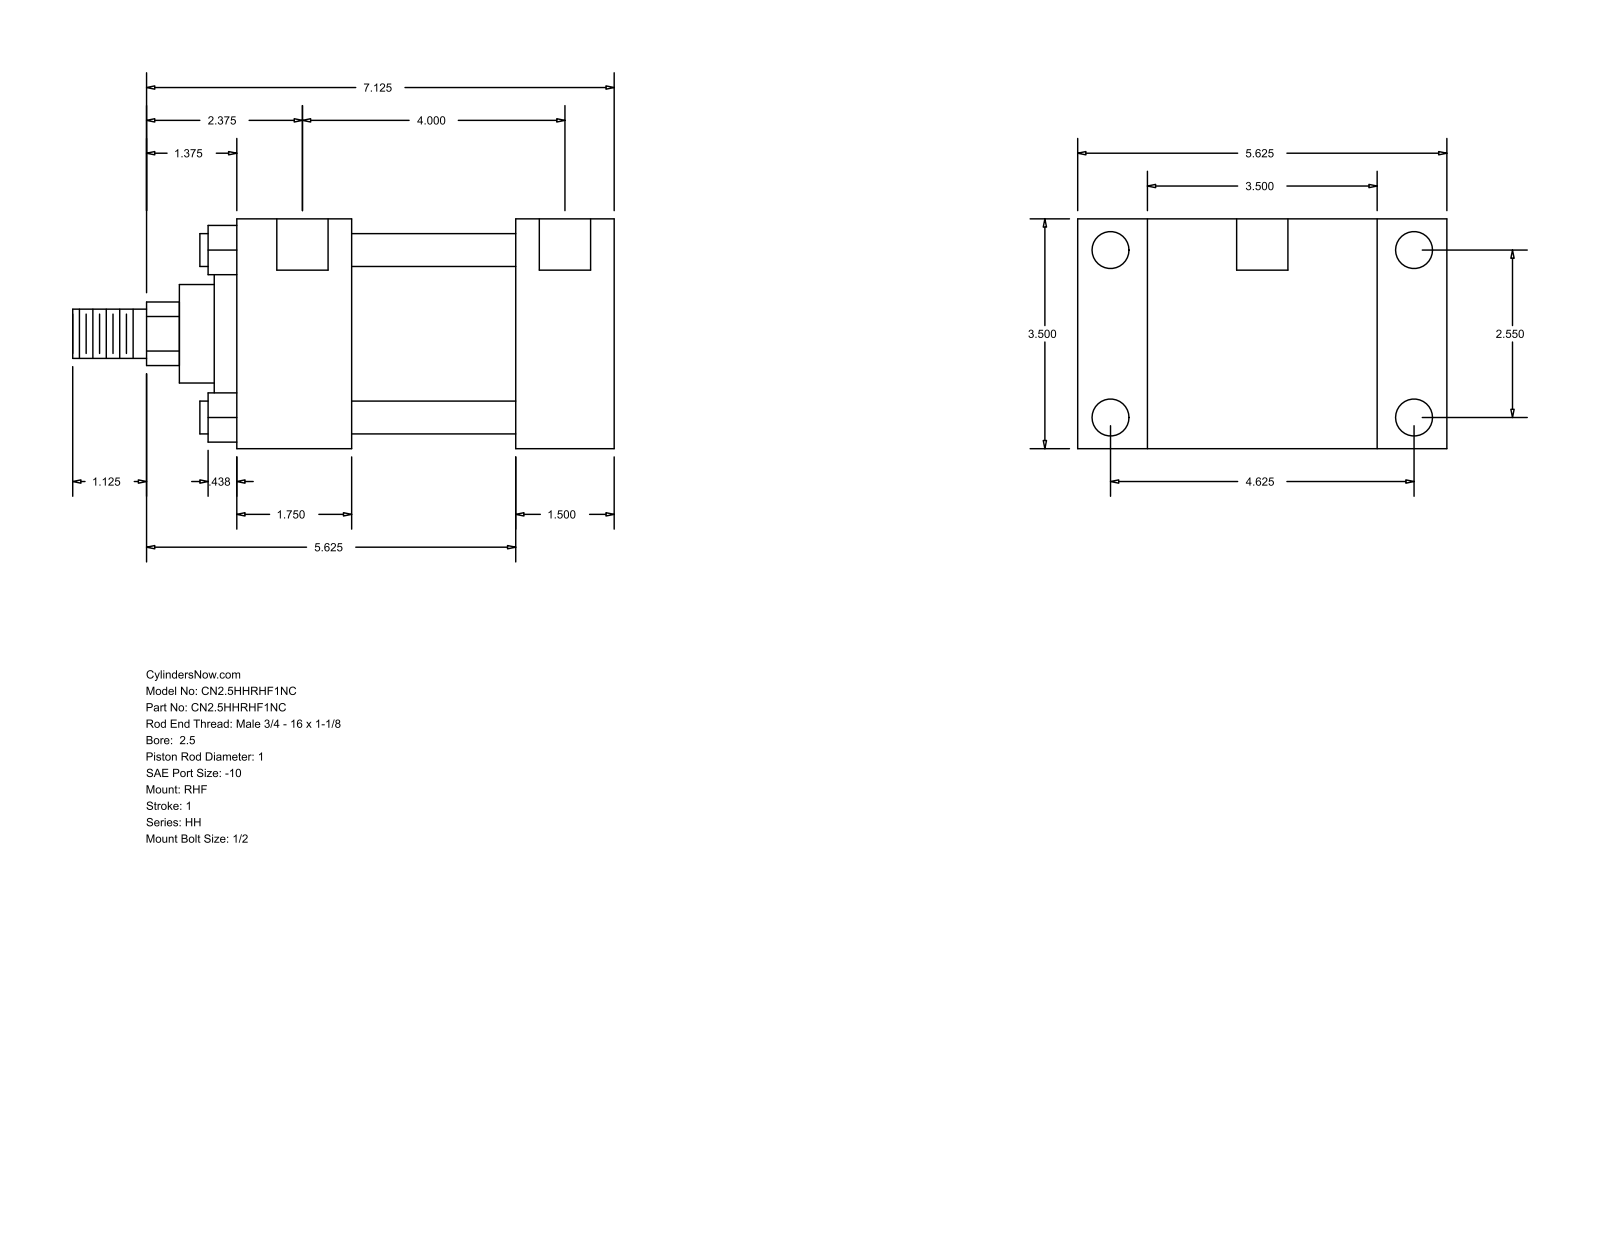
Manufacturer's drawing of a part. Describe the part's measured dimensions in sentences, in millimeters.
The part is named "HH_RHF__0250_1". Its 3-D file was written by "GSSL Pune (CONFIG_CONTROL_DESIGN)". It is 0 solids with 90 faces: 61 planar, 29 cylindrical and 0 other. Overall it measures 209.55 by 142.88 by 88.9 millimeters. Round holes: 4 of diameter 5.56, 4 of diameter 14.3, 2 of diameter 19.84. Round bosses or shafts: 4 of diameter 12.7, 1 of diameter 73.03, 1 of diameter 60.33, 1 of diameter 38.1, 1 of diameter 25.4, 1 of diameter 19.05. Partial cylindrical surfaces (rounded edges, fillets, slot ends): 1 of radius 12.29. The main face-to-face distances are 88.9, 38.09, 26.99, 115.89, 107.96, 146.05, 142.88, 44.46, 63.5, 101.59. The hole center spacings are 64.76, 104.77, 117.48, 134.15, 1.58, 1.59, 101.6, 103.18.
